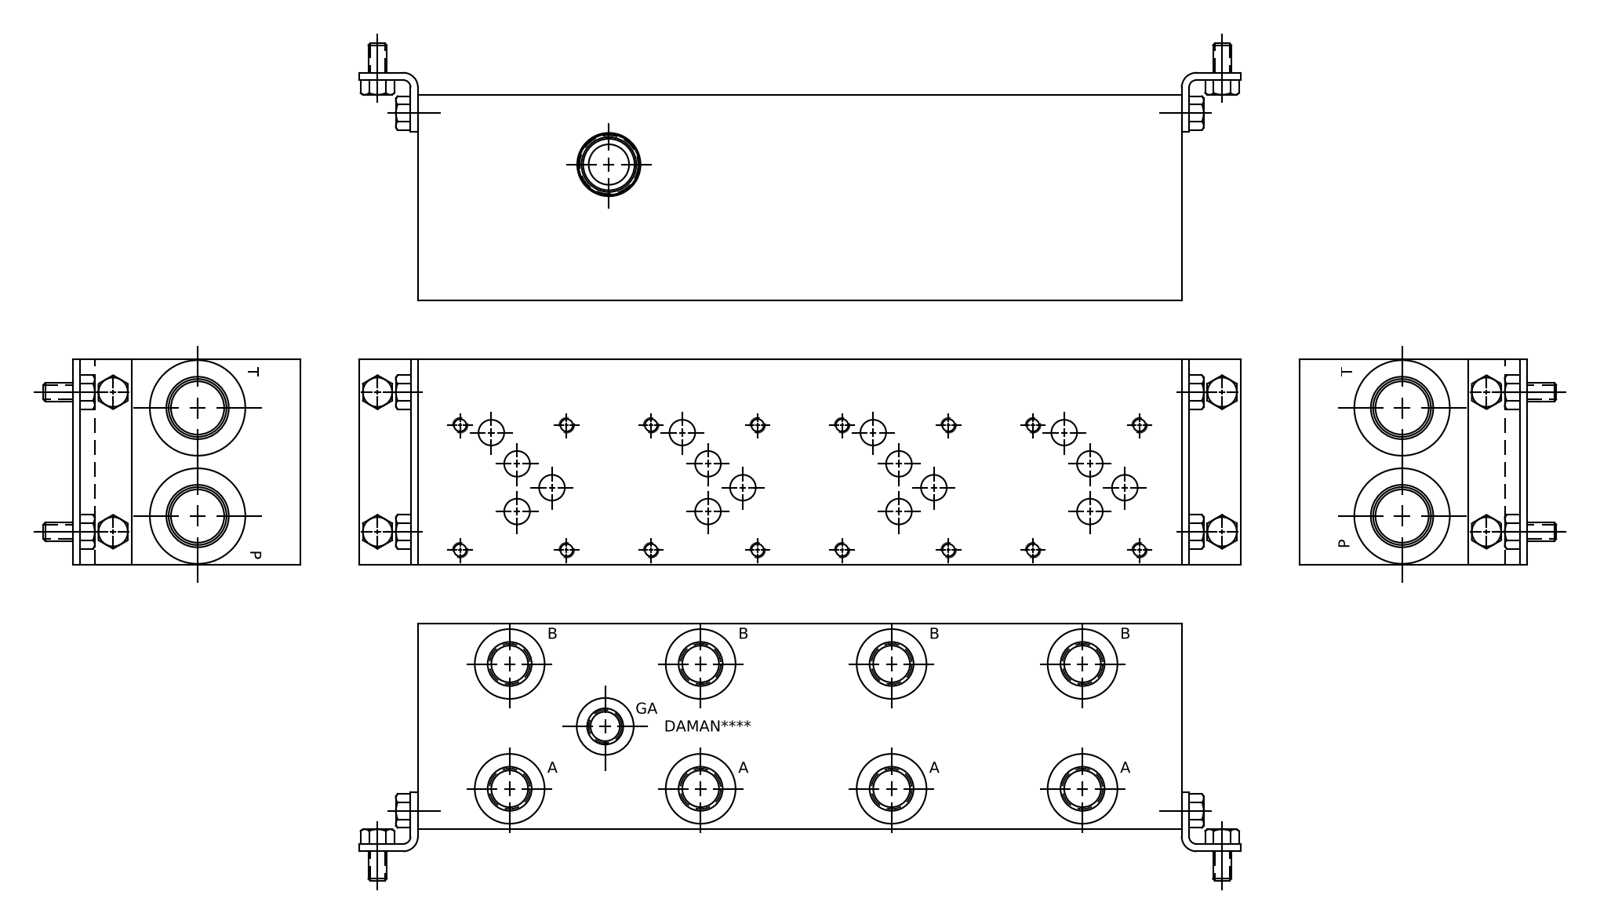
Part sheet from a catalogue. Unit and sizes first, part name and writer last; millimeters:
Units: millimetres
Overall size (bounding box): 330.2 × 88.9 × 88.9
Round holes (diameter × count): ⌀5.11 ×16, ⌀6.35 ×16, ⌀11.13 ×16, ⌀15.88 ×8, ⌀17.5 ×8, ⌀19.05 ×8, ⌀19.25 ×8, ⌀30.63 ×8, ⌀6.53 ×2, ⌀7.92 ×2, ⌀23.01 ×2, ⌀24.92 ×2
Main face-to-face distances: 88.9, 0.79, 330.2, 88.11, 329.41, 328.62, 19.05, 15.06, 14.27, 73.84
Hole centre spacings: 82.55, 165.1, 98.63, 70.95, 18.27, 46.05, 53.98, 68.25
Volume: 2 435 000 mm³ · Surface area: 169 649 mm²
Bodies: 1 solid, 858 faces (442 planar, 127 cylindrical, 289 other)
Part name (STEP PRODUCT): Part_AD05P043S_S_3D
STEP written by: Autodesk Inventor 2020 (AUTOMOTIVE_DESIGN)
